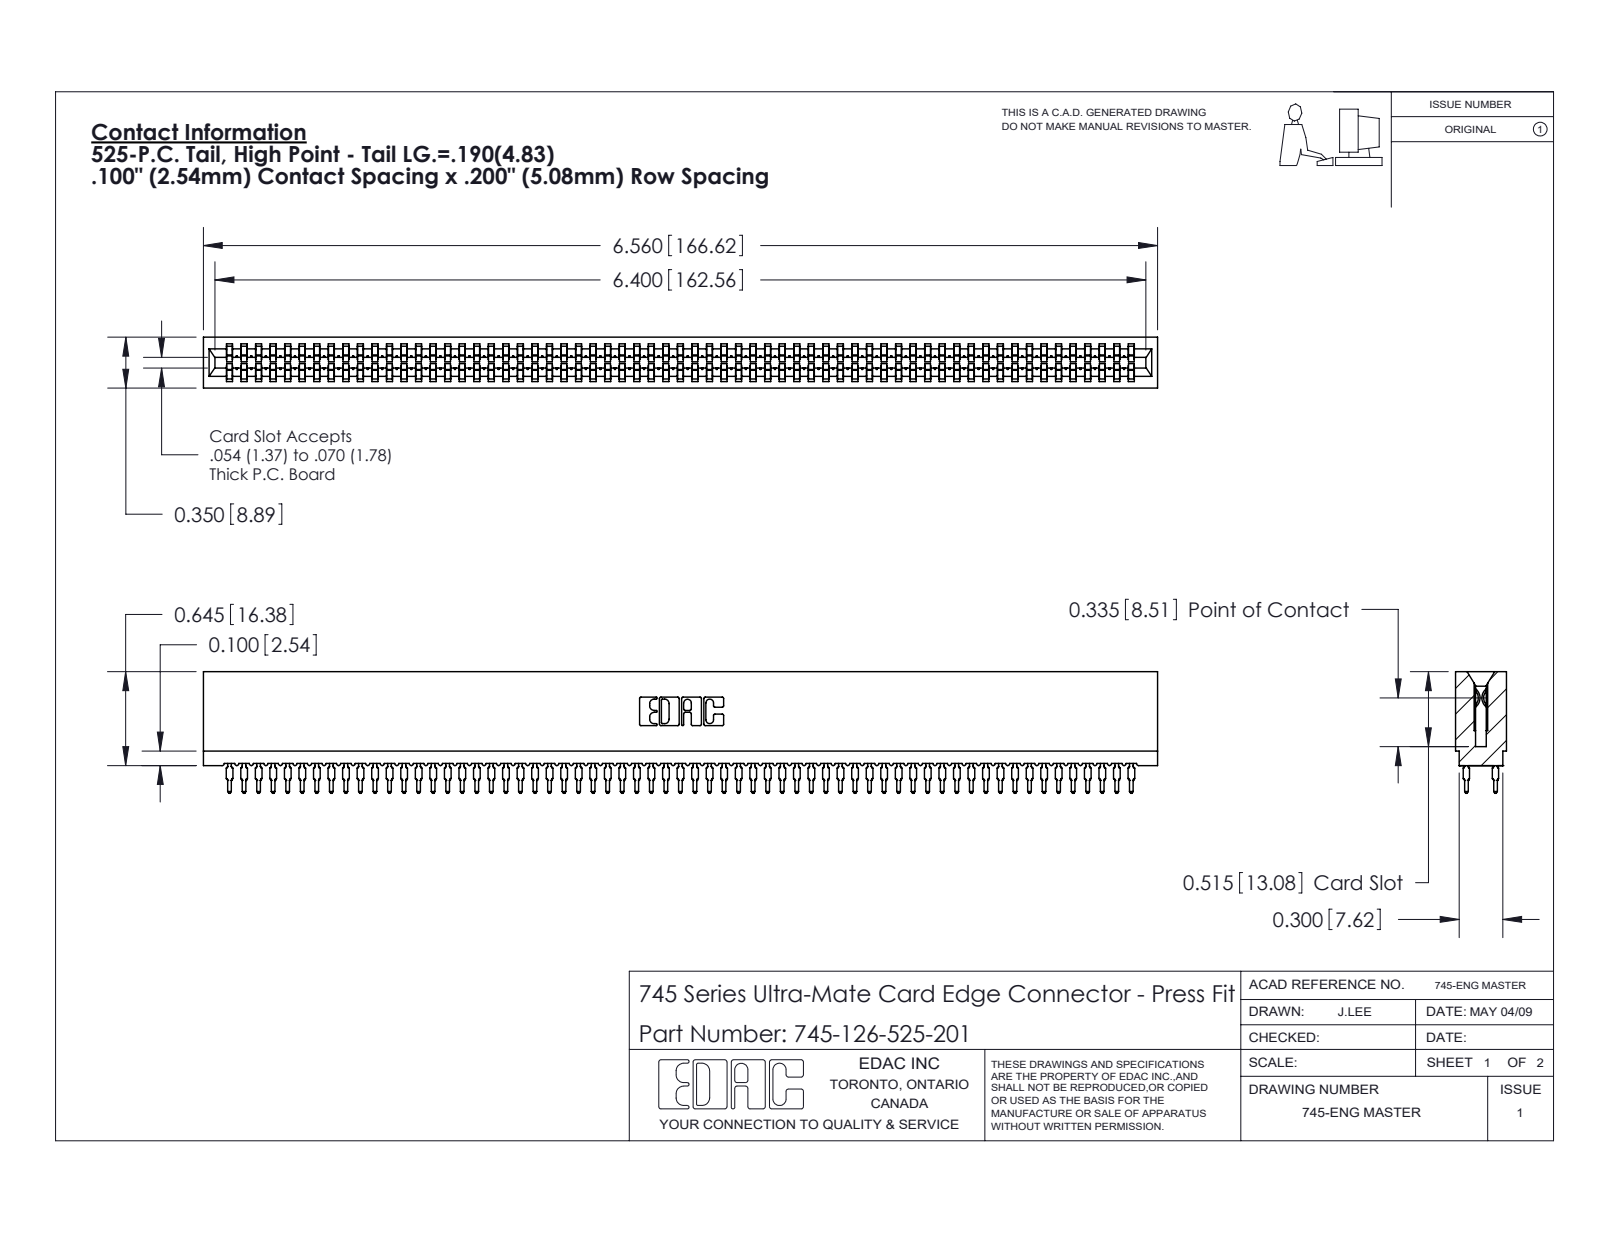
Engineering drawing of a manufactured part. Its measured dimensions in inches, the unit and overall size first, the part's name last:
Units: inches
Overall size (bounding box): 6.56 × 0.836 × 0.35
Partial cylindrical surfaces — rounded edges, fillets, slot ends (radius × count): R0.021 ×252, R0.015 ×126, R0.01 ×22, R0.005 ×8, R0.011 ×8, R0.007 ×6, R0.031 ×6, R0.026 ×3
Main face-to-face distances: 0.35, 0.063, 0.287, 0.045, 0.305, 0.018, 0.243, 0.138, 0.212, 0.093
Volume: 0.906 in³ · Surface area: 47.35 in²
Bodies: 127 solids, 11372 faces (5851 planar, 2245 cylindrical, 3276 other)
Part name (STEP PRODUCT): 745-126-525-201; 745 Part_Insulator Option - 01; 745-292-001_525
STEP written by: SolidWorks 2020 (CONFIG_CONTROL_DESIGN)
